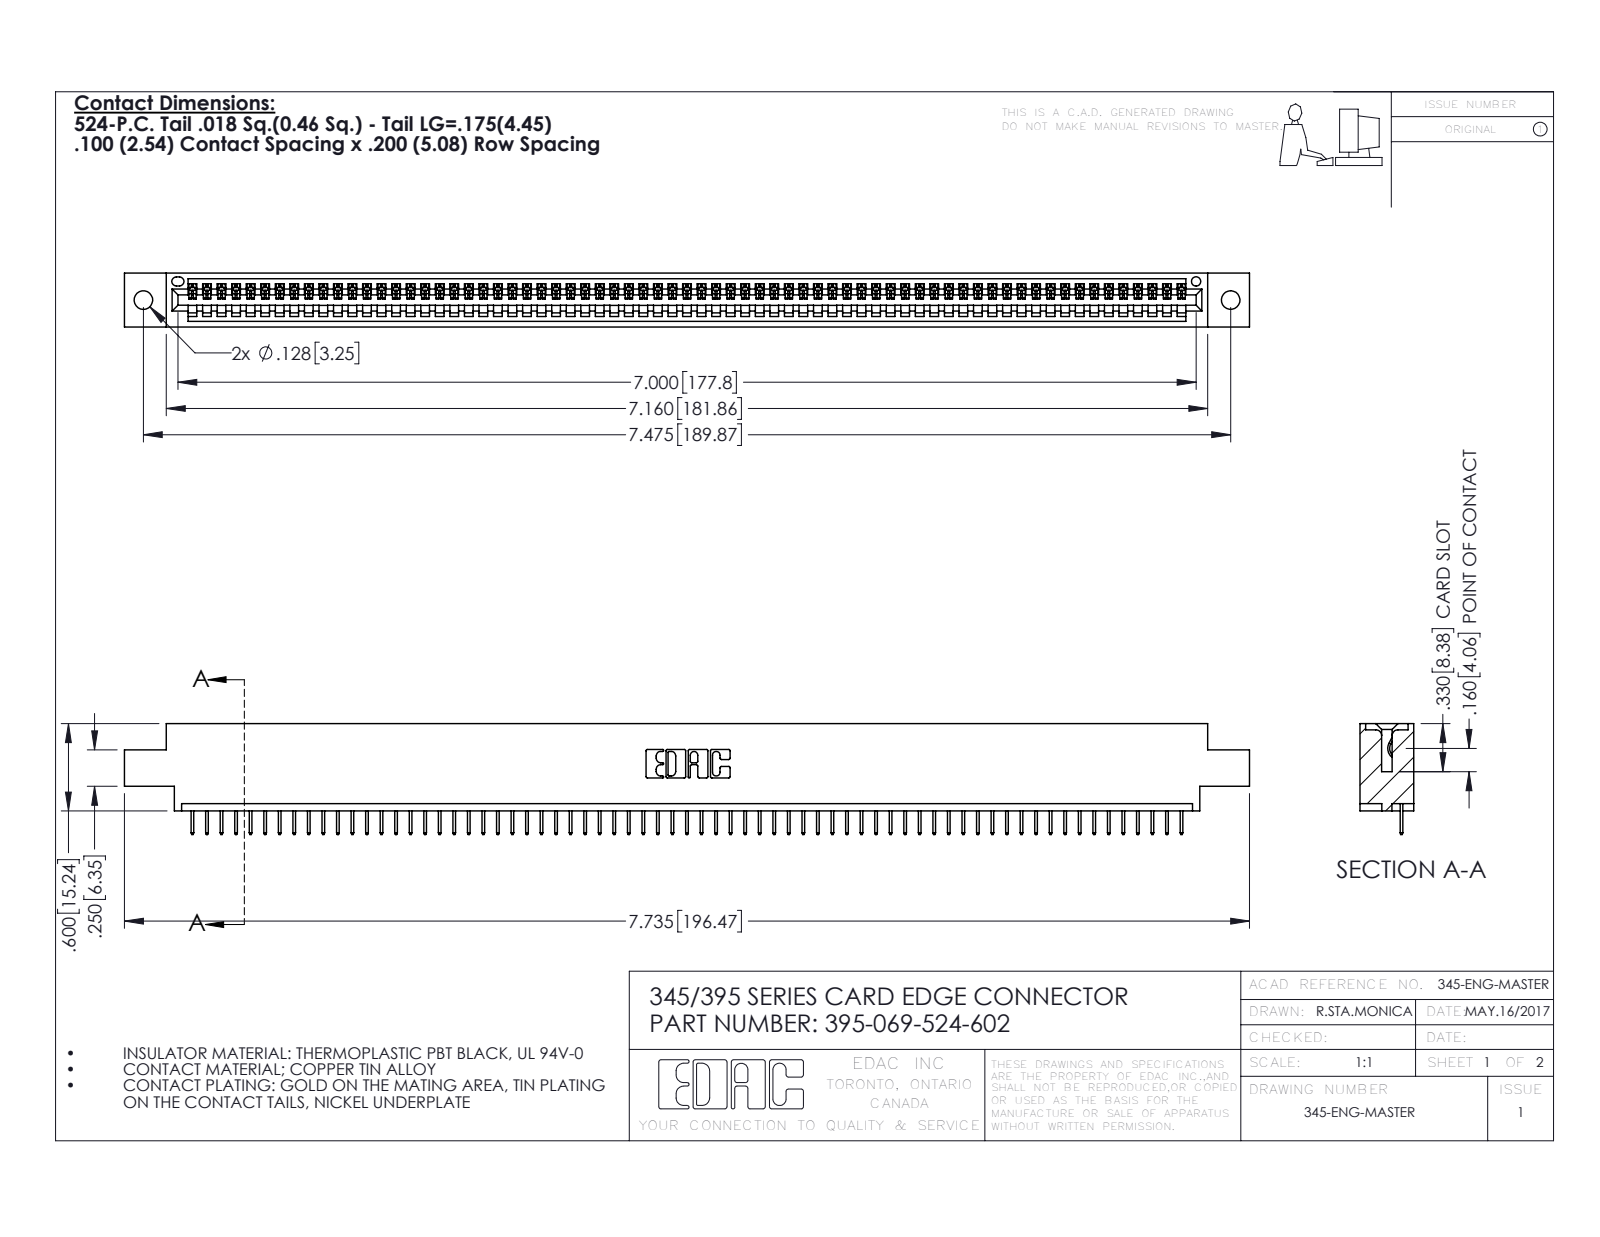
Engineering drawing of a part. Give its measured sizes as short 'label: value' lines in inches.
name: 345 Part_0.170 Offset - 0.128 Dia; 395-069-524-602; 345-292-001_345-293-124
written by: SolidWorks 2016 (CONFIG_CONTROL_DESIGN)
unit: in
bodies: 70 solids, 4408 faces (3258 planar, 1150 cylindrical, 0 other)
size: 7.735 × 0.762 × 0.37
volume: 1.126 in³; area: 37.02 in²
holes: 2× ⌀0.128, 1× ⌀0.064
rounds: 138× R0.006, 22× R0.01, 6× R0.007, 6× R0.031, 3× R0.026, 2× R0.031, 2× R0.04, 1× R0.014
face distances: 0.072, 0.298, 0.37, 0.2, 0.098, 0.272, 0.025, 0.225, 0.072, 0.175
hole spacings: 0.27, 7.239, 7.475
